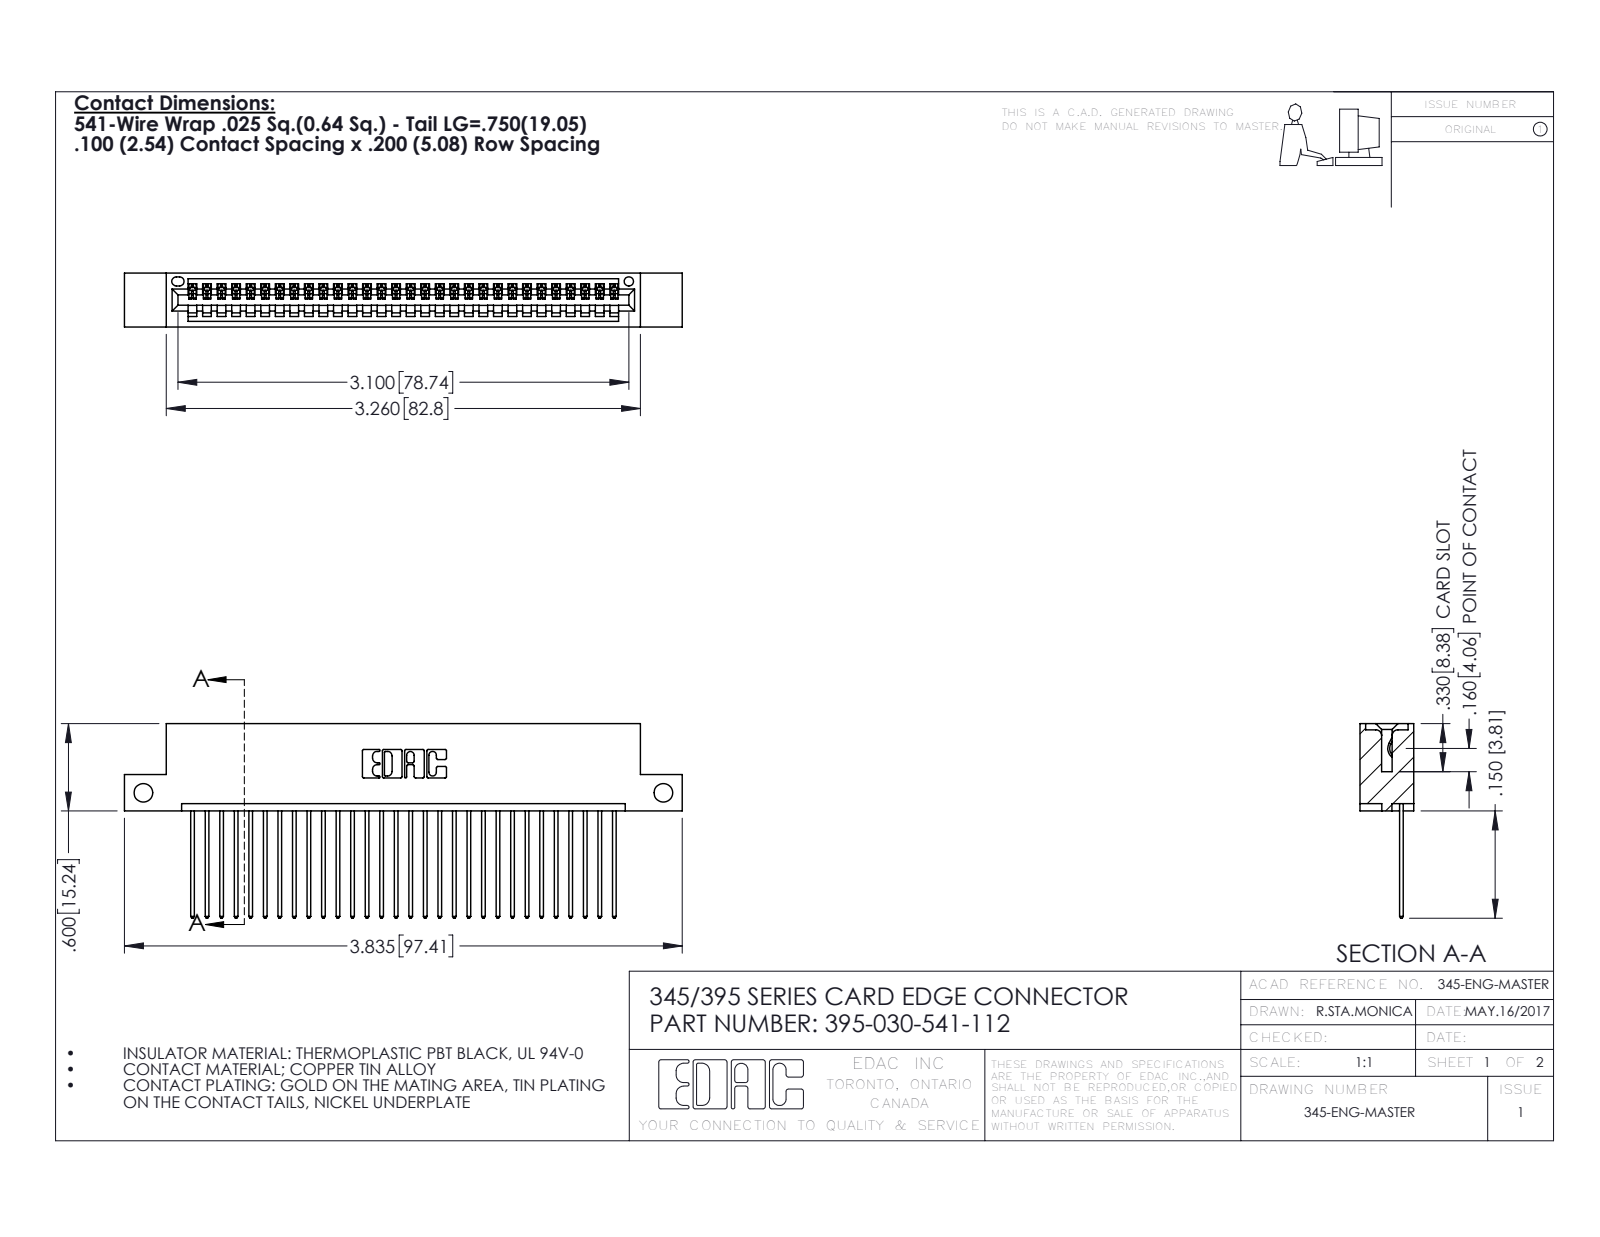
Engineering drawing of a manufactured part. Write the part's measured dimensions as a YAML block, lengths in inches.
part_name: "345 Part_Flush Mounting Lugs - Side Mount; 395-030-541-112; 345-292-001_345-293-141"
step_written_by: "SolidWorks 2016 (CONFIG_CONTROL_DESIGN)"
units: inches
bodies: {solids: 31, faces: 1866, planar: 1280, cylindrical: 586, other: 0}
overall_size: [3.835, 1.337, 0.37]
volume: 0.559
surface_area: 19.31
round_holes:
  - {diameter: 0.128, count: 2}
  - {diameter: 0.064, count: 1}
partial_cylinders:
  - {radius: 0.006, count: 60}
  - {radius: 0.01, count: 60}
  - {radius: 0.01, count: 22}
  - {radius: 0.007, count: 6}
  - {radius: 0.031, count: 6}
  - {radius: 0.026, count: 3}
  - {radius: 0.031, count: 2}
  - {radius: 0.04, count: 2}
face_to_face_distances: [0.072, 0.298, 0.2, 0.098, 0.272, 0.025, 0.37, 0.225, 0.149, 0.072]
hole_center_spacings: [3.575]
